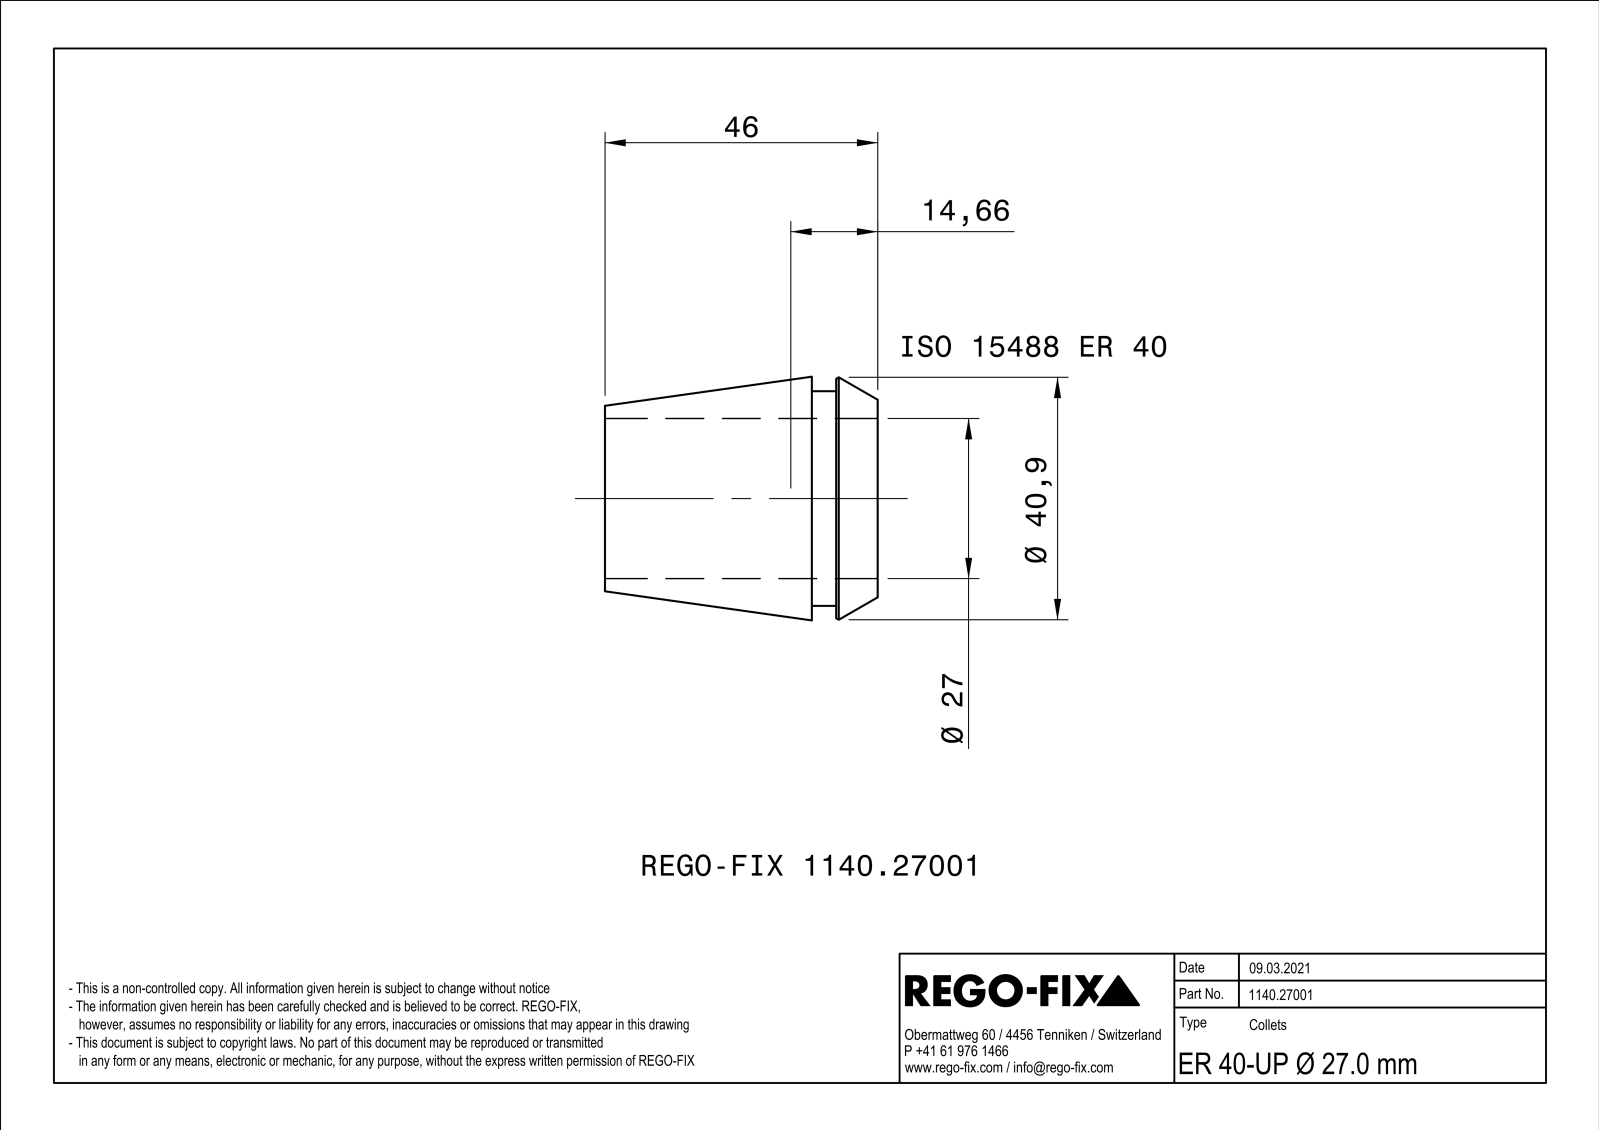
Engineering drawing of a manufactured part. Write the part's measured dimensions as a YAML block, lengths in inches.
part_name: "NOCUT"
step_written_by: "SIEMENS PLM Software Solid Edge ST10 (AUTOMOTIVE_DESIGN)"
units: inches
bodies: {solids: 1, faces: 177, planar: 88, cylindrical: 9, other: 80}
overall_size: [1.811, 1.614, 1.614]
volume: 1.126
surface_area: 23.3
round_holes:
  - {diameter: 1.063, count: 1}
round_bosses_or_shafts:
  - {diameter: 1.425, count: 1}
face_to_face_distances: [0.039, 0.437, 0.276, 0.161, 1.811, 1.535, 1.374, 0.295, 0.02, 0.142]
